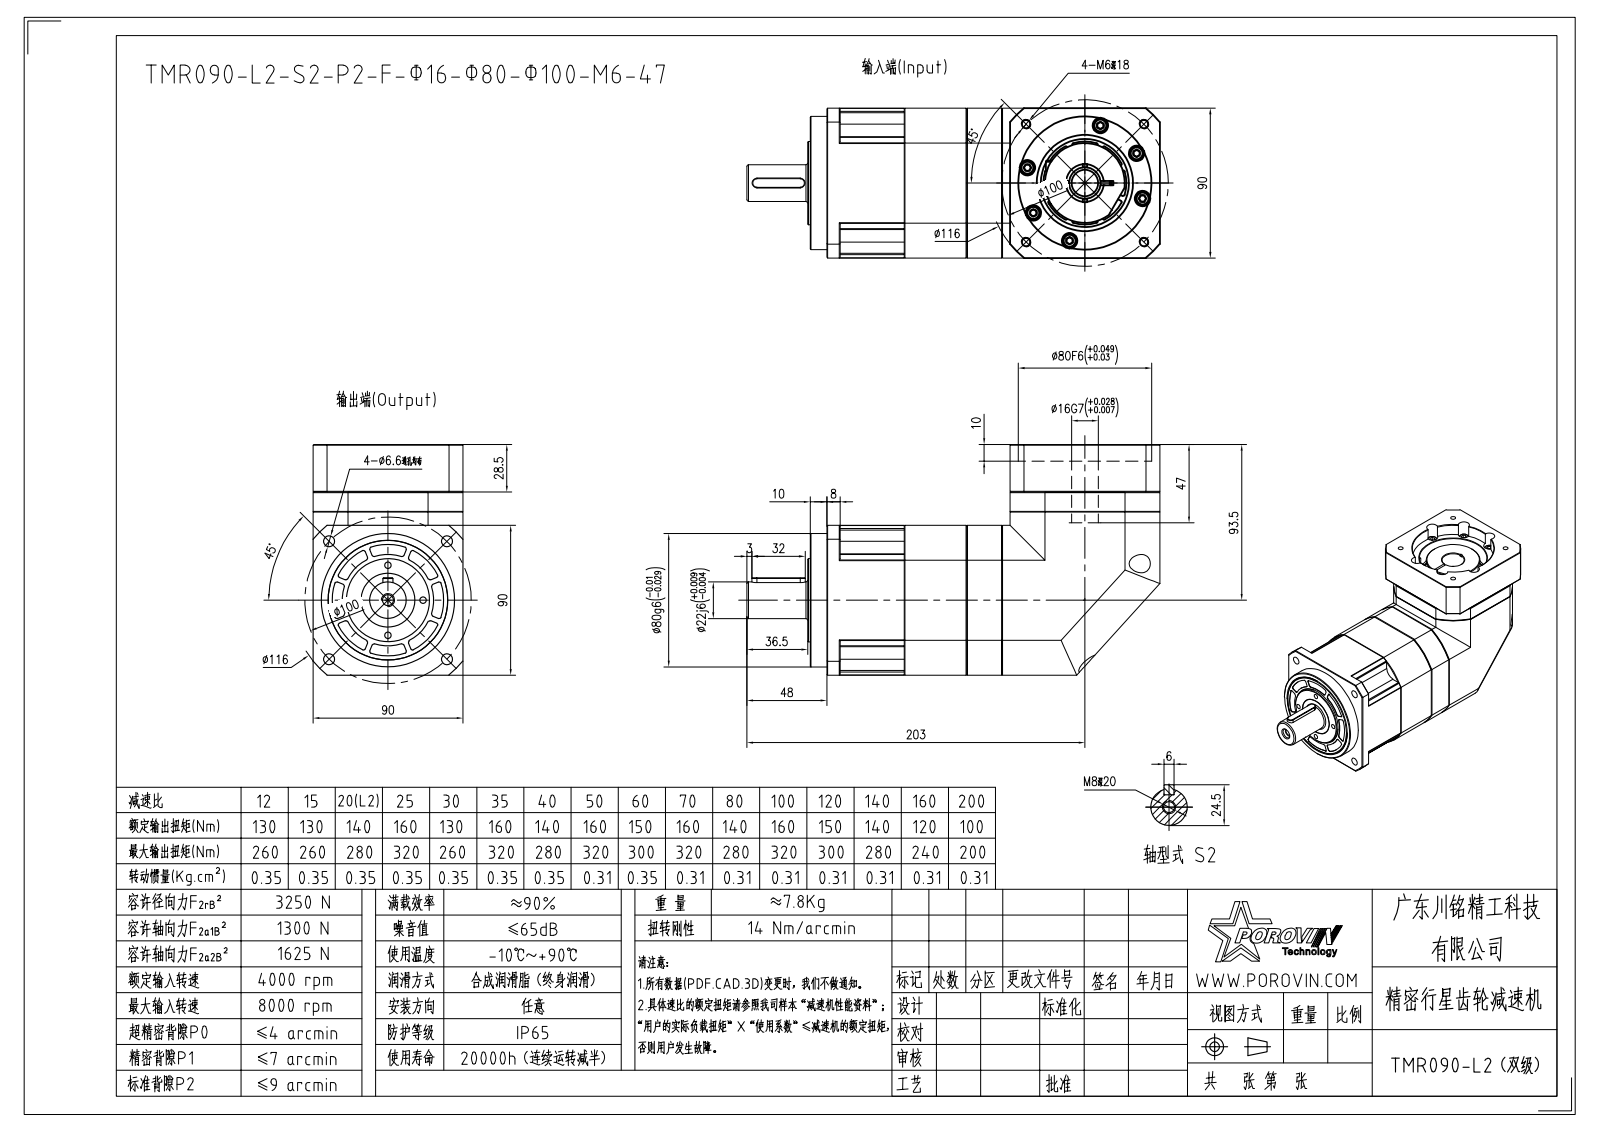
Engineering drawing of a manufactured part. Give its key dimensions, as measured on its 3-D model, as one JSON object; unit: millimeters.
{"part_name": "HEXAGON_SOCKET_HEAD_CAP_SCR-935; HEX_SOCKET_SET_SCREWS_WITH_FLAT; SPRING_LOCK_WASHERS--NORM-20979; SPRING_LOCK_WASHERS--NORMAL-834 (+8 more)", "step_written_by": "CREO PARAMETRIC BY PTC INC, 2020053 (CONFIG_CONTROL_DESIGN)", "units": "millimeters", "bodies": {"solids": 44, "faces": 1333, "planar": 530, "cylindrical": 564, "other": 239}, "overall_size": [248, 138.5, 90], "volume_mm3": 1602000, "surface_area_mm2": 240589, "round_holes": [[5.4, 12], [5.5, 12], [9.5, 12], [6.6, 10], [4.2, 7], [5, 5], [6.5, 5], [4, 4], [6.68, 4], [11, 4], [6.8, 1], [8.4, 1]], "round_bosses_or_shafts": [[8.5, 12], [8, 12], [5, 12], [10, 4], [9.88, 4], [6, 4], [80, 1], [78, 1]], "partial_cylinders_radius": [[1, 92], [7.5, 4], [51, 3], [3, 2], [58, 2], [4, 1], [5.25, 1], [20.75, 1]], "face_to_face_distances": [90, 12, 21.5, 21.3, 37.5, 58.8, 59, 110, 10, 98], "hole_center_spacings": [35.75, 27.36, 38.16, 44, 50.01, 66.06, 66.53, 70.72]}
